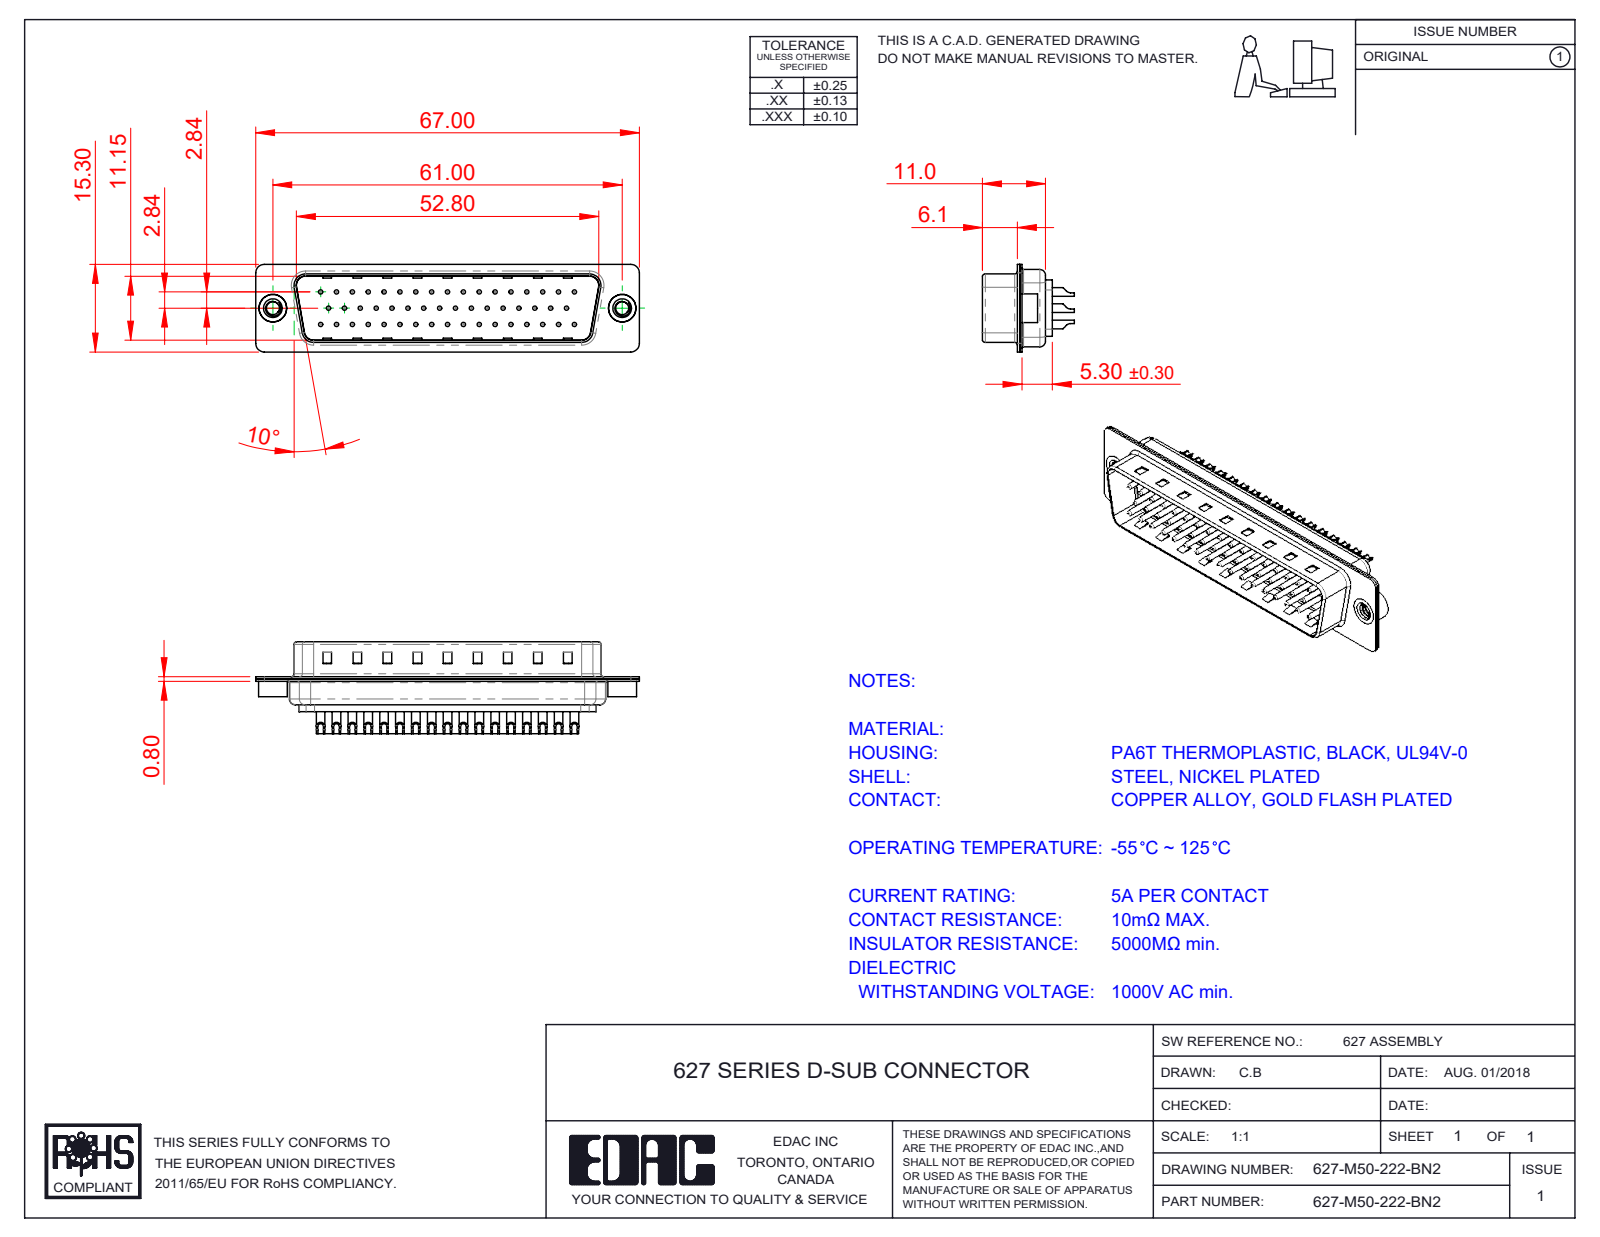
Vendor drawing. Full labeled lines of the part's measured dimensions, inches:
Part name (STEP PRODUCT): 627M Shell Front_50 Contacts; 627M Contact Row 2_22L; 627M Shell Rear_50 Contacts; 627M Contact Row 1_22 (+4 more)
STEP written by: SolidWorks 2020 (CONFIG_CONTROL_DESIGN)
Units: inches
Bodies: 55 solids, 2262 faces (653 planar, 941 cylindrical, 668 other)
Overall size (bounding box): 2.638 × 0.632 × 0.602
Volume: 0.283 in³ · Surface area: 17.31 in²
Round holes (diameter × count): ⌀0.03 ×50, ⌀0.039 ×50, ⌀0.063 ×50, ⌀0.079 ×50, ⌀0.089 ×2, ⌀0.157 ×2, ⌀0.189 ×2
Round bosses / shafts (diameter × count): ⌀0.059 ×50, ⌀0.197 ×2, ⌀0.193 ×2
Partial cylindrical surfaces — rounded edges, fillets, slot ends (radius × count): R0.059 ×16, R0.079 ×12, R0.02 ×8, R0.063 ×8, R0.039 ×7, R0.01 ×4, R0.024 ×4, R0.026 ×4
Main face-to-face distances: 0.016, 0.455, 0.224, 0.24, 0.031, 0.03, 0.485, 0.485, 0.516, 0.209
Hole centre spacings: 0.124, 0.109, 0.218, 0.327, 0.436, 0.545, 0.654, 0.198
